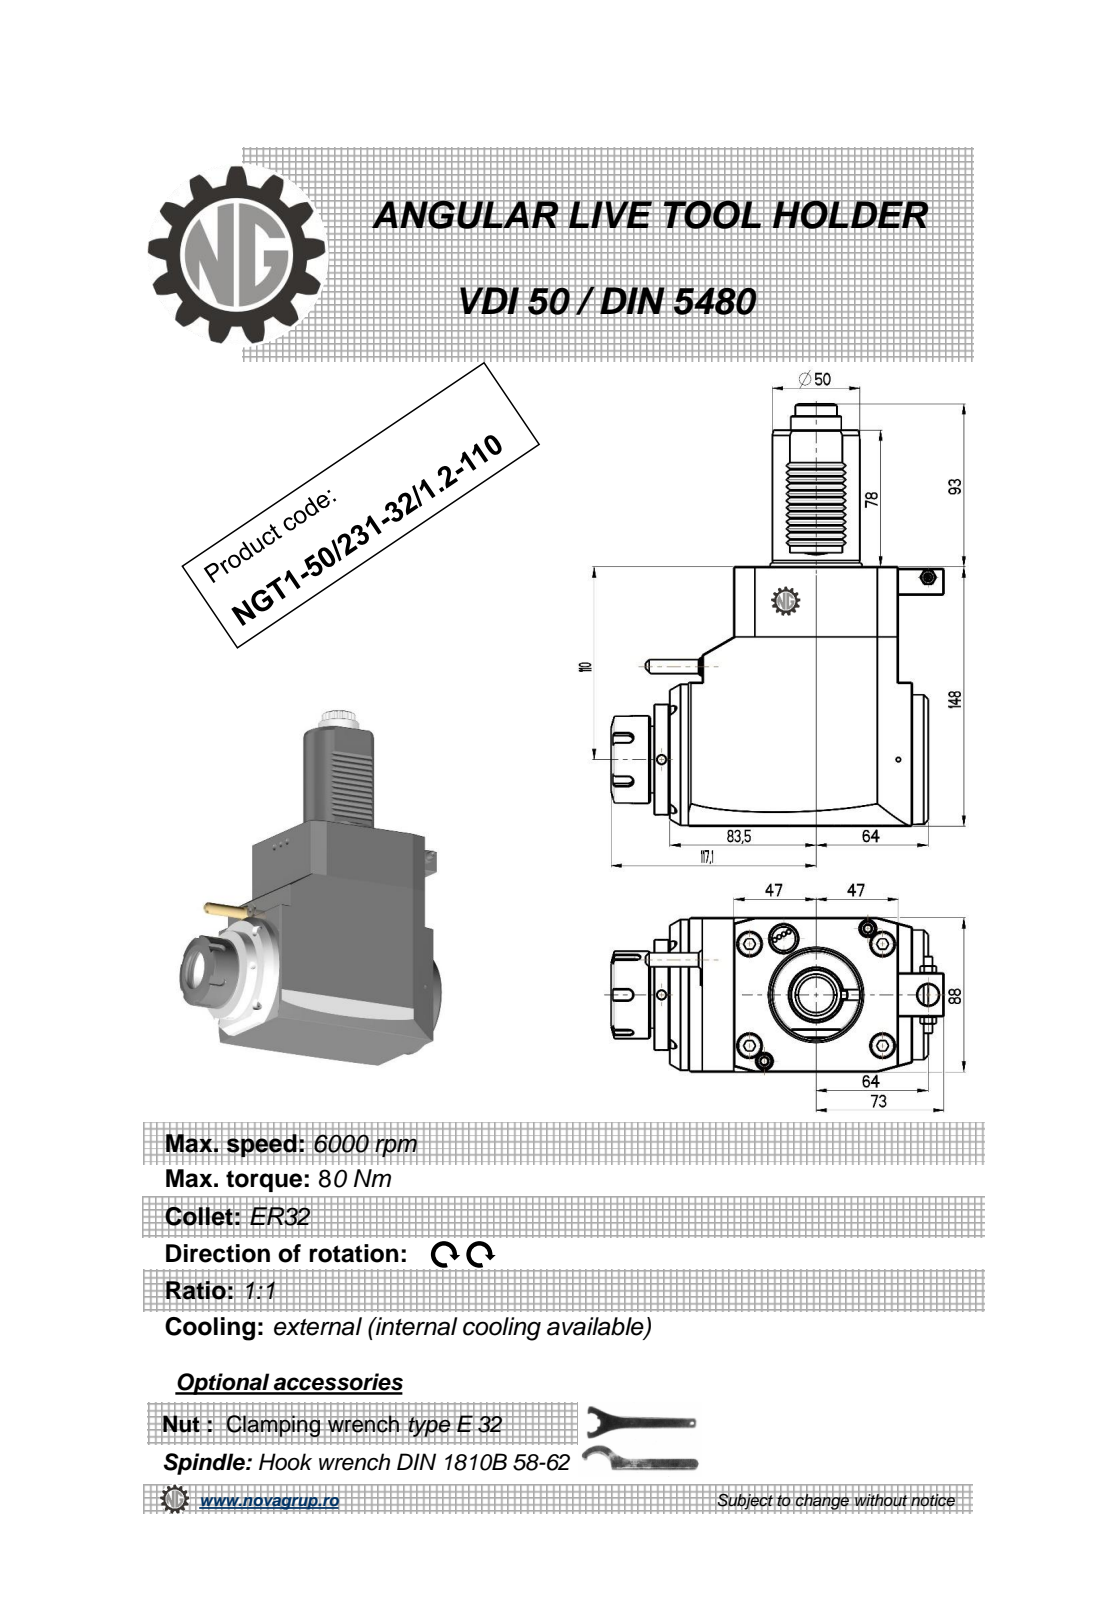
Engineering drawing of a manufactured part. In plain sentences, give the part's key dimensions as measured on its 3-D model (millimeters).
The part is named "NGT1_50_231_32_1_2_110". Its 3-D file was written by "PRO/ENGINEER BY PARAMETRIC TECHNOLOGY CORPORATION, 2010280 (CONFIG_CONTROL_DESIGN)". It is 1 solid with 506 faces: 194 planar, 157 cylindrical and 155 other. Overall it measures 241 by 190.1 by 89.6 millimeters. Its volume is 1 811 000 cubic millimeters and its surface area 111 934 square millimeters. Round holes: 3 of diameter 5, 1 of diameter 3, 1 of diameter 4.2, 1 of diameter 9.5, 1 of diameter 12, 1 of diameter 27. Round bosses or shafts: 2 of diameter 50, 1 of diameter 86, 1 of diameter 74, 1 of diameter 63, 1 of diameter 50.5, 1 of diameter 41, 1 of diameter 28.8, 1 of diameter 10. Partial cylindrical surfaces (rounded edges, fillets, slot ends): 36 of radius 3.04, 12 of radius 0.26, 12 of radius 0.3, 6 of radius 0.2, 5 of radius 3, 1 of radius 10.56, 1 of radius 11.88, 1 of radius 17.5. The main face-to-face distances are 88, 148, 147.5, 9, 94, 17, 8, 111, 120, 36.5. The hole center spacings are 52.46, 56.65, 101.5, 152.25, 184.38.
